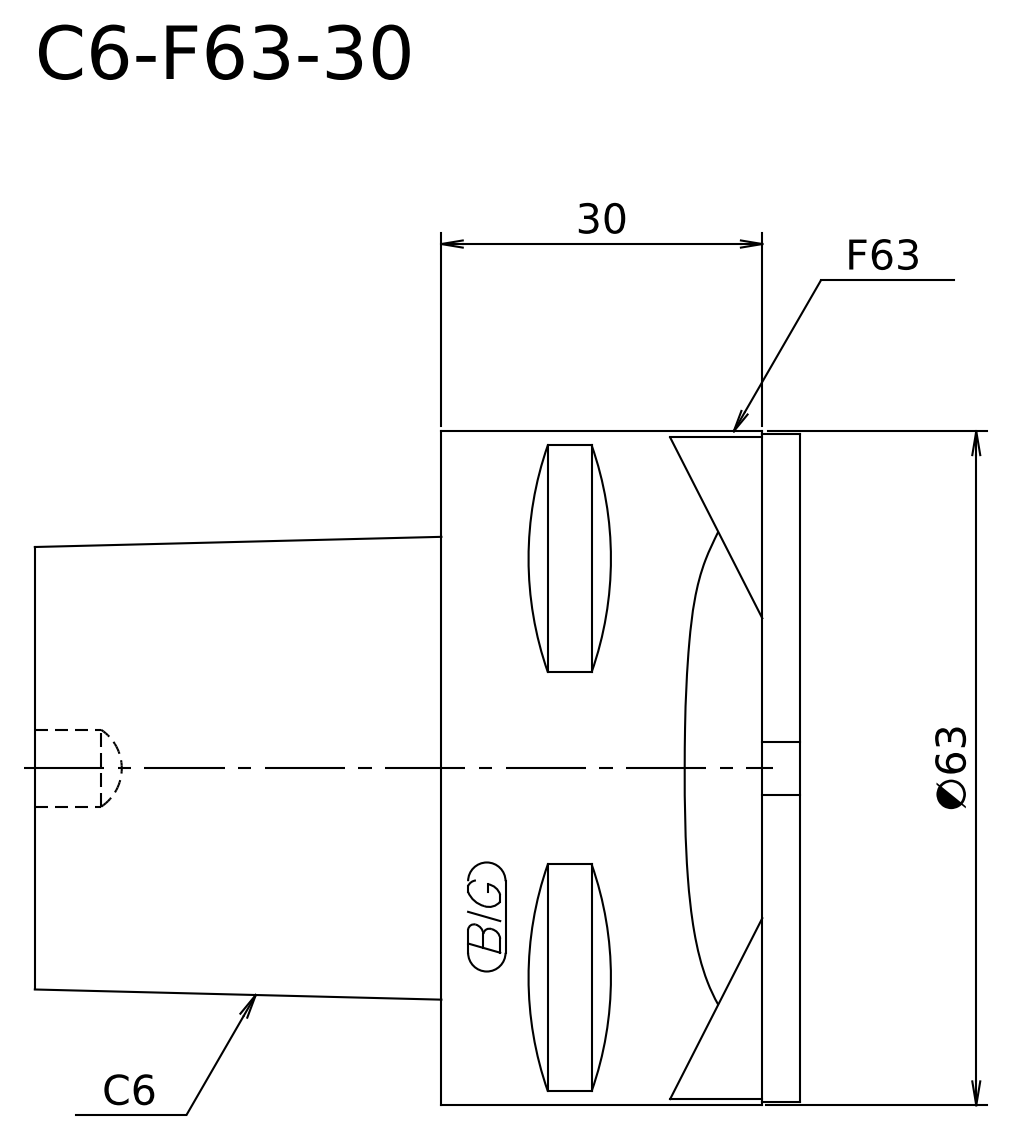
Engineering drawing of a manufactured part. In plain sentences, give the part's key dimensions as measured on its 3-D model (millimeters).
The part is named "C6-F63-30". Its 3-D file was written by "SolidWorks 2021 (CONFIG_CONTROL_DESIGN)". It is 1 solid with 7 faces: 3 planar, 2 cylindrical and 2 other. Overall it measures 68 by 63 by 63 millimeters. Its volume is 146 956 cubic millimeters and its surface area 17 099 square millimeters. Round bosses or shafts: 1 of diameter 63. The main face-to-face distances are 30, 38, 68.
